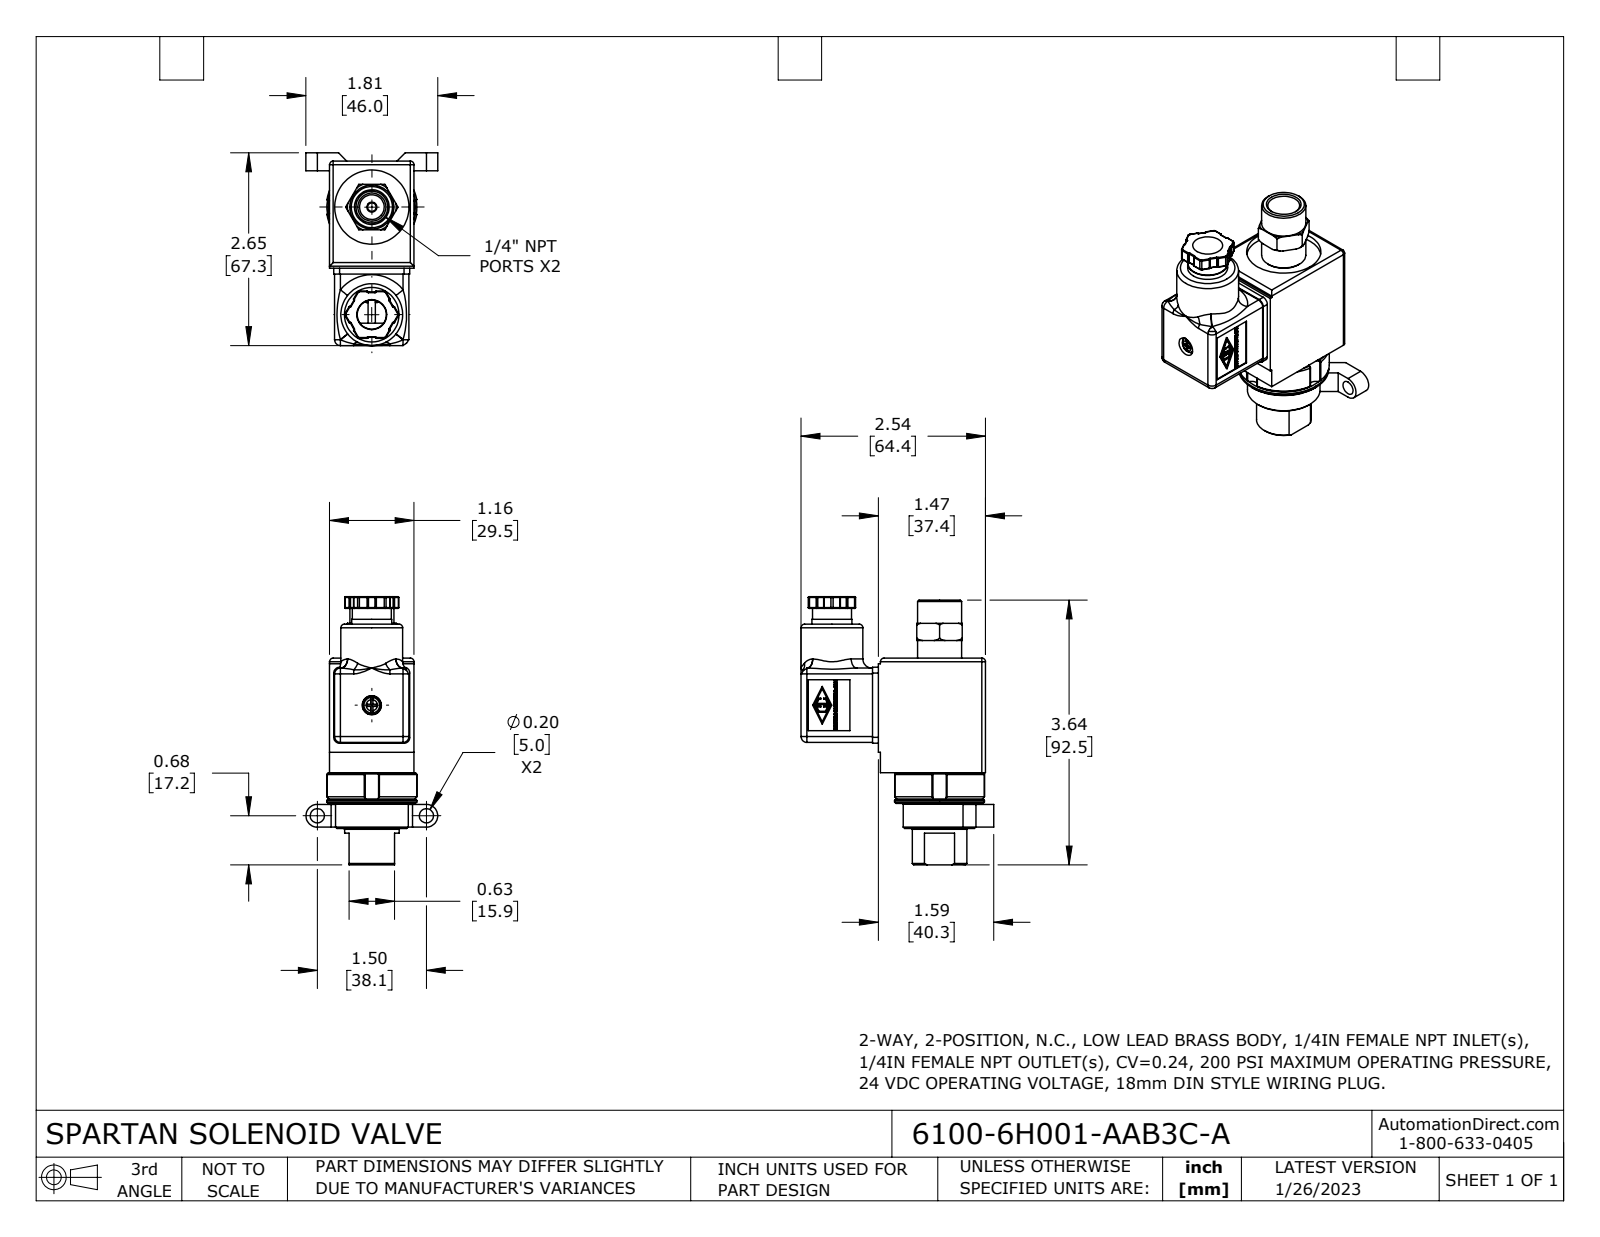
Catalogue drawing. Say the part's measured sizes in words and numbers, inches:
The part is named "6100-6H001-AAB3C-A". Its 3-D file was written by "SolidWorks 2021 (CONFIG_CONTROL_DESIGN)". It is 2 solids with 1289 faces: 625 planar, 208 cylindrical and 456 other. Overall it measures 3.687 by 2.649 by 1.812 inches. Its volume is 3.772 cubic inches and its surface area 45.23 square inches. Round holes: 2 of diameter 0.195, 1 of diameter 0.053, 1 of diameter 0.06, 1 of diameter 0.085, 1 of diameter 0.102, 1 of diameter 0.118, 1 of diameter 0.137, 1 of diameter 0.203, 1 of diameter 0.236, 1 of diameter 0.263, 1 of diameter 0.339, 1 of diameter 0.4. Round bosses or shafts: 1 of diameter 1.236, 1 of diameter 1, 1 of diameter 0.85, 1 of diameter 0.75, 1 of diameter 0.606, 1 of diameter 0.535, 1 of diameter 0.512, 1 of diameter 0.451. Partial cylindrical surfaces (rounded edges, fillets, slot ends): 56 of radius 0.01, 12 of radius 0.08, 10 of radius 0.05, 6 of radius 0.03, 4 of radius 0.008, 4 of radius 0.02, 4 of radius 0.04, 4 of radius 0.094. The main face-to-face distances are 1.161, 0.048, 0.973, 0.925, 1.472, 0.079, 1.031, 0.118, 1.043, 1.043. The hole center spacings are 0.281, 0.352, 1.127, 1.161, 1.478, 1.5, 1.505, 1.694.
